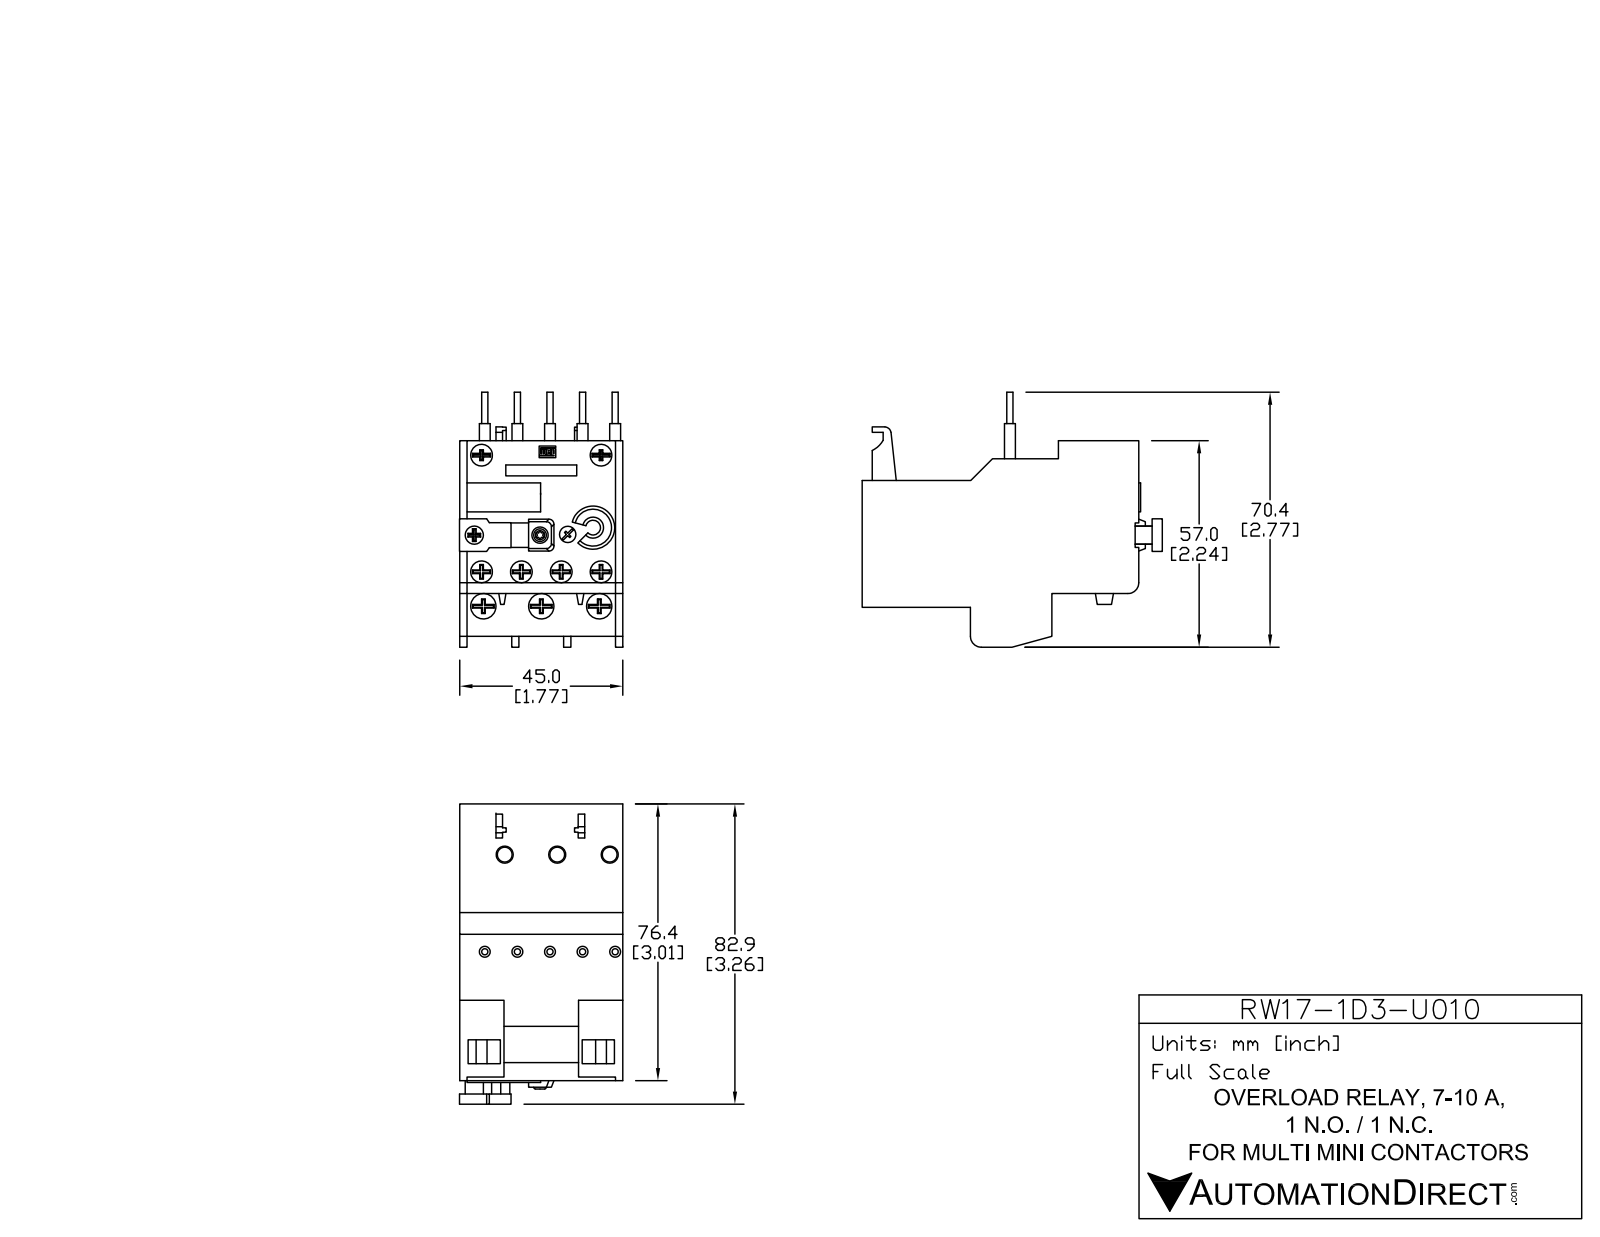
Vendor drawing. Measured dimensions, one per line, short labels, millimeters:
name: RW17D-1D3-U010
written by: SolidWorks 2013 (AUTOMOTIVE_DESIGN)
unit: mm
bodies: 18 solids, 756 faces (515 planar, 214 cylindrical, 27 other)
size: 82.65 × 70.5 × 45.55
volume: 127 454 mm³; area: 34 704 mm²
holes: 6× ⌀6, 3× ⌀4, 3× ⌀7, 3× ⌀7.5, 1× ⌀4.5, 1× ⌀4.75, 1× ⌀5.33, 1× ⌀5.5, 1× ⌀10.42
bosses: 7× ⌀5.5, 7× ⌀3, 5× ⌀1.75, 2× ⌀5.6, 2× ⌀3.25, 1× ⌀6.42, 1× ⌀6.15, 1× ⌀4.75
rounds: 20× R0.5, 12× R0.25, 9× R1, 6× R4.52, 4× R5.86, 4× R7.86, 3× R1.5, 2× R1.25
face distances: 45.5, 1.5, 10.85, 11, 76.4, 35, 1.42, 74.98, 74.9, 6
hole spacings: 15, 8.55, 10.75, 30, 10.57, 11.86, 14.25, 21.35
